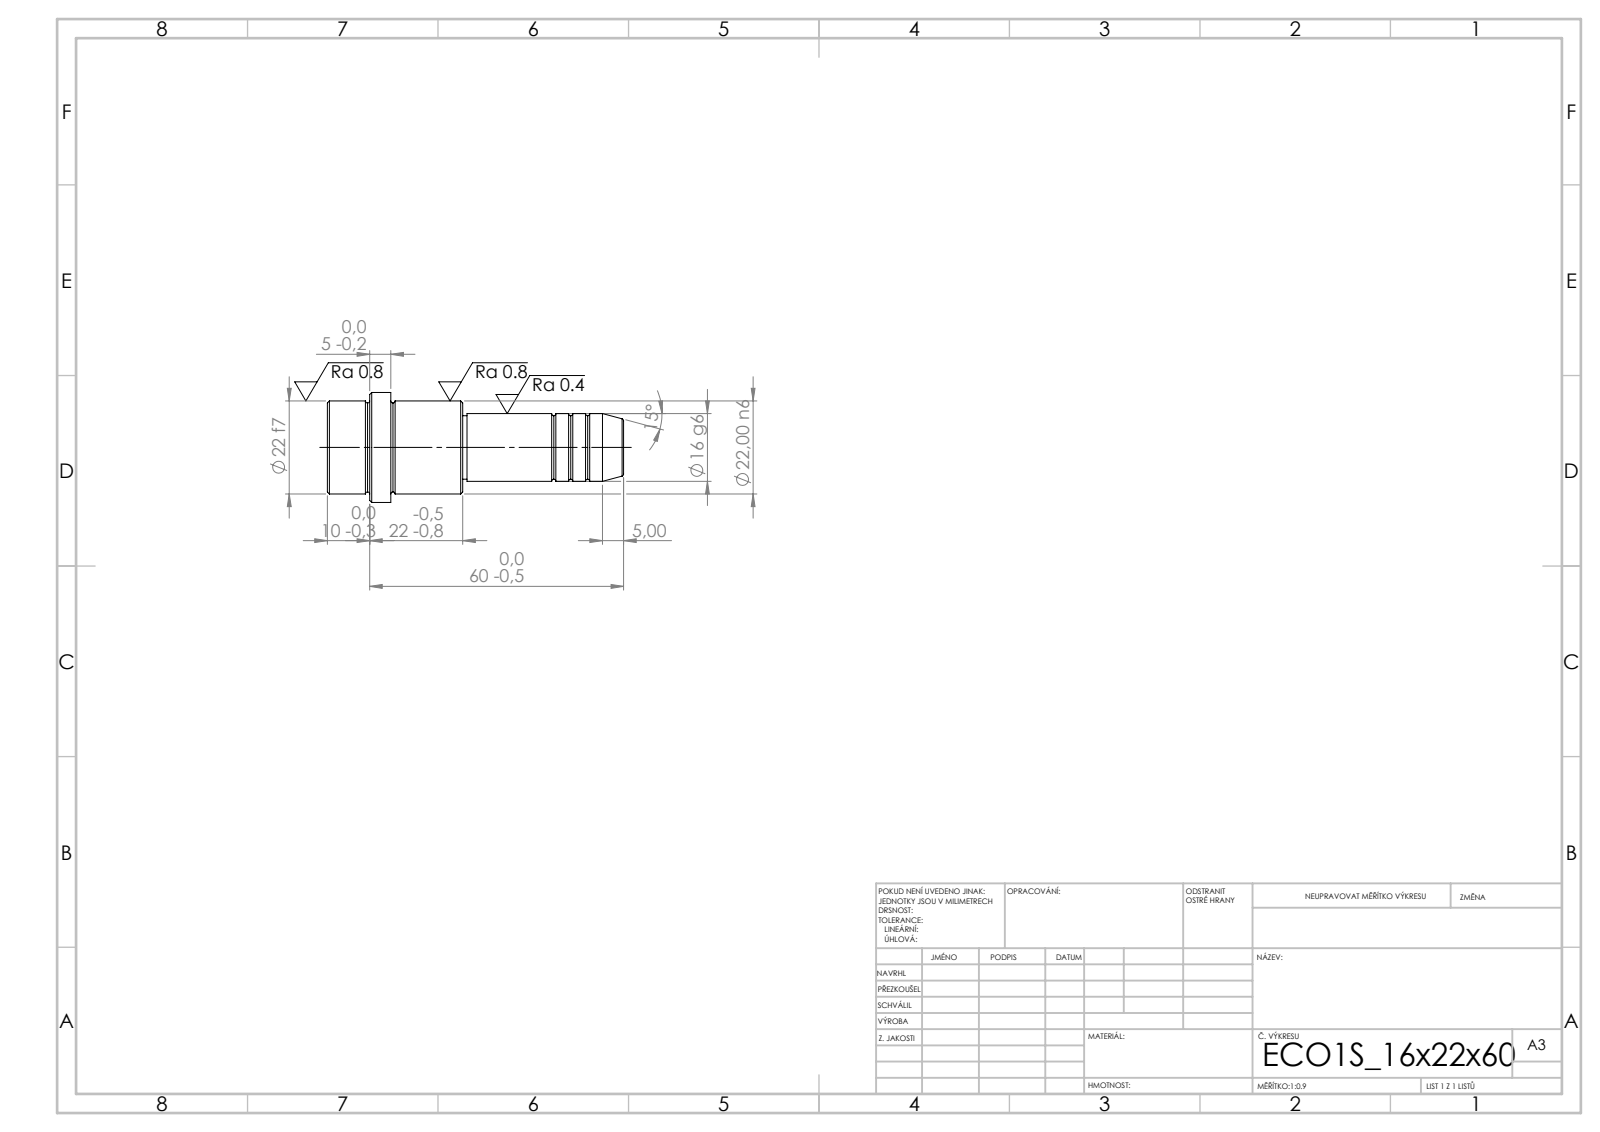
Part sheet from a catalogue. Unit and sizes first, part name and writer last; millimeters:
Units: millimetres
Overall size (bounding box): 70 × 26 × 26
Round bosses / shafts (diameter × count): ⌀26 ×1, ⌀22 ×1, ⌀16 ×1, ⌀15 ×1
Main face-to-face distances: 32, 17, 15, 38, 55, 70, 60, 22, 5, 10
Volume: 20 236 mm³ · Surface area: 5 296 mm²
Bodies: 1 solid, 52 faces (6 planar, 16 cylindrical, 30 other)
STEP written by: SolidWorks 2019 (CONFIG_CONTROL_DESIGN)
